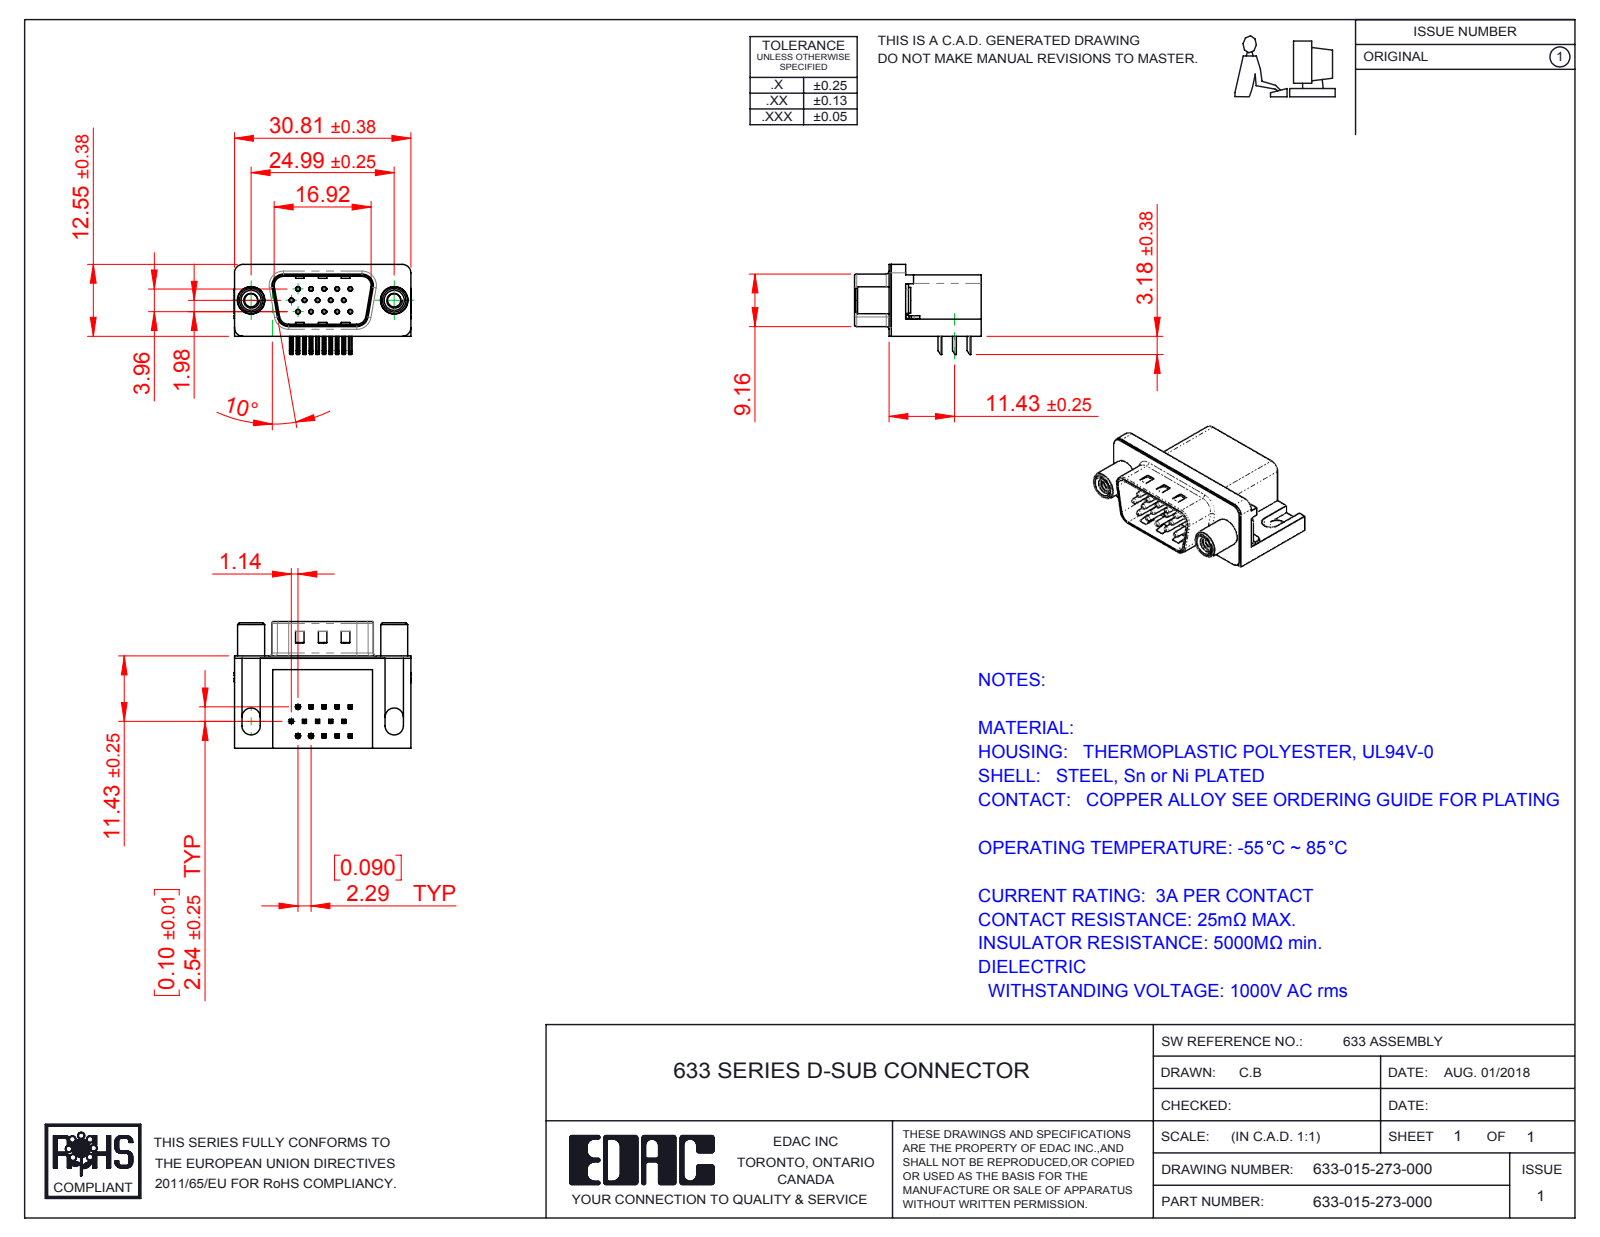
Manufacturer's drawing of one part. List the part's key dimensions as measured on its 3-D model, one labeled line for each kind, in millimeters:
Part name (STEP PRODUCT): 633-015-273-000; 633 Contact Middle_Recessed; 633 Contact Bottom; 633 Round Threaded Standoff (+5 more)
STEP written by: SolidWorks 2016 (CONFIG_CONTROL_DESIGN)
Units: millimetres
Bodies: 21 solids, 1433 faces (853 planar, 447 cylindrical, 133 other)
Overall size (bounding box): 30.89 × 22.1 × 15.73
Volume: 4 116 mm³ · Surface area: 5 397 mm²
Round holes (diameter × count): ⌀0.35 ×15, ⌀0.8 ×15, ⌀2.3 ×2, ⌀3.1 ×2, ⌀4 ×2, ⌀4.8 ×2, ⌀5 ×2
Round bosses / shafts (diameter × count): ⌀0.75 ×15, ⌀4.9 ×2, ⌀4.7 ×2, ⌀4.5 ×2, ⌀3.85 ×2
Partial cylindrical surfaces — rounded edges, fillets, slot ends (radius × count): R0.25 ×60, R0.12 ×30, R1 ×16, R0.5 ×9, R1.6 ×8, R1.5 ×7, R0.9 ×4, R2 ×4
Main face-to-face distances: 0.4, 10.35, 15.7, 2.9, 6.7, 2.5, 16.1, 0.35, 10.7, 13.2
Hole centre spacings: 3.96, 2.28, 4.57, 2.29, 6.05, 6.86, 7.92, 6.04
